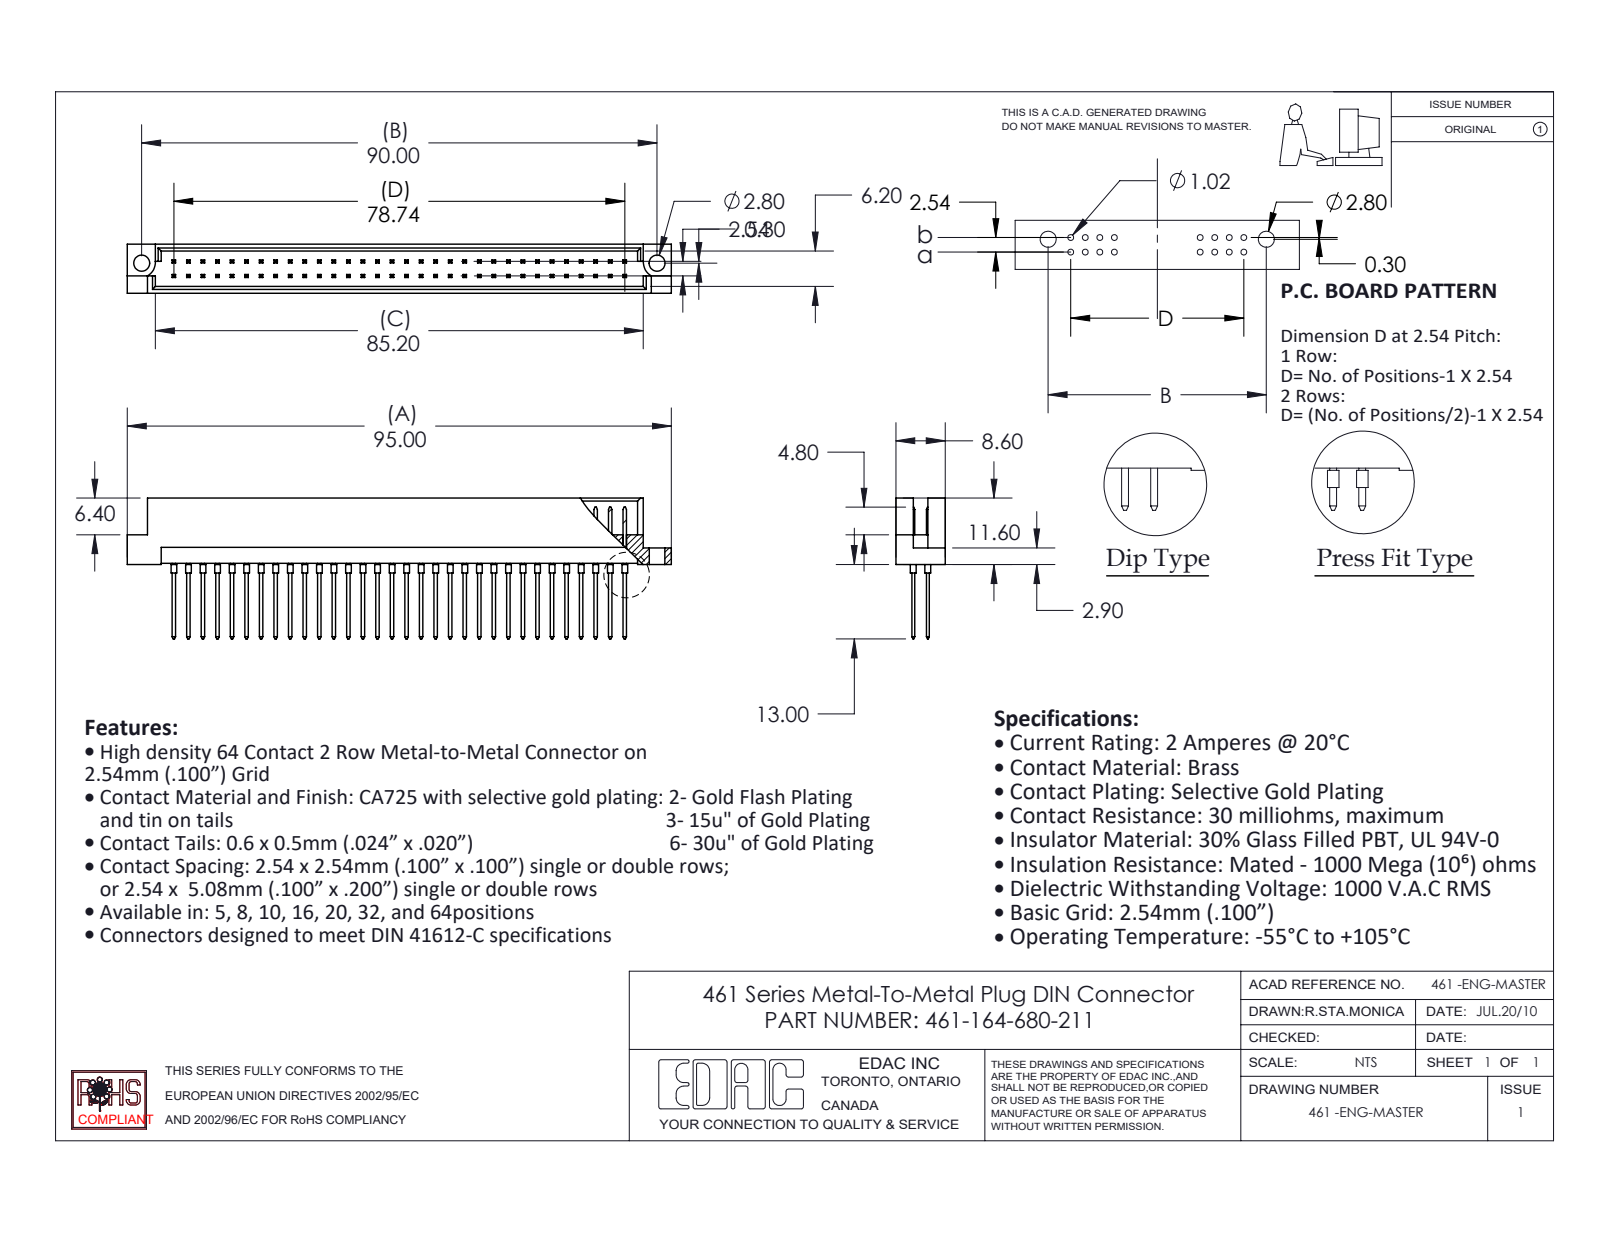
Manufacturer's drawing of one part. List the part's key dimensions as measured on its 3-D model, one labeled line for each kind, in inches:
Part name (STEP PRODUCT): 461-164-680-211; 461 Part_64; 461-290_80
STEP written by: SolidWorks 2020 (CONFIG_CONTROL_DESIGN)
Units: inches
Bodies: 65 solids, 1713 faces (1578 planar, 135 cylindrical, 0 other)
Overall size (bounding box): 3.74 × 0.969 × 0.339
Volume: 0.313 in³ · Surface area: 14.01 in²
Round holes (diameter × count): ⌀0.11 ×2
Round bosses / shafts (diameter × count): ⌀0.039 ×64
Partial cylindrical surfaces — rounded edges, fillets, slot ends (radius × count): R0.11 ×2
Main face-to-face distances: 0.047, 0.291, 0.1, 0.129, 0.209, 0.082, 0.162, 0.109, 0.229, 0.062
Hole centre spacings: 3.543
